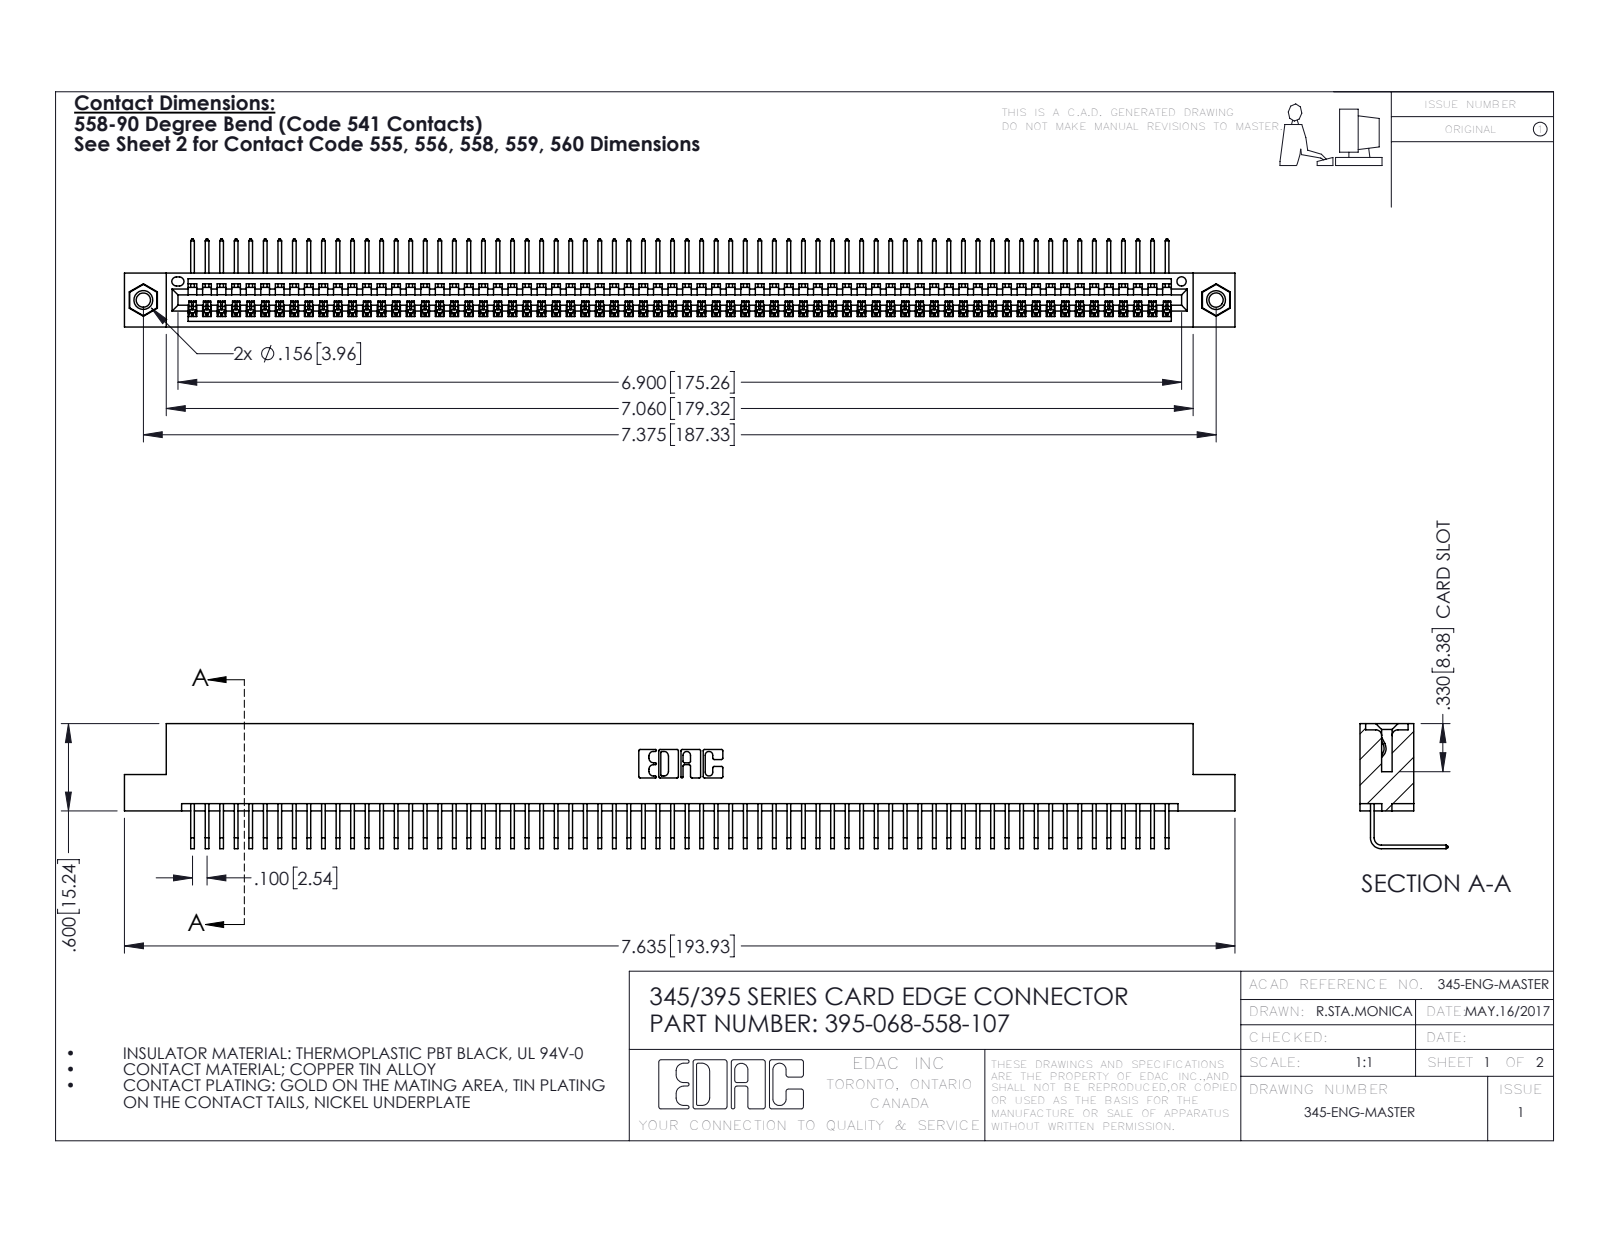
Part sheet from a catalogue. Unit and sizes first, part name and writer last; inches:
Units: inches
Overall size (bounding box): 7.635 × 0.859 × 0.605
Round holes (diameter × count): ⌀0.098 ×2, ⌀0.125 ×2, ⌀0.156 ×2, ⌀0.064 ×1
Round bosses / shafts (diameter × count): ⌀0.155 ×2
Partial cylindrical surfaces — rounded edges, fillets, slot ends (radius × count): R0.006 ×136, R0.01 ×22, R0.007 ×6, R0.031 ×6, R0.026 ×3, R0.031 ×2, R0.04 ×2, R0.014 ×1
Main face-to-face distances: 0.072, 0.298, 0.37, 0.2, 0.098, 0.272, 0.025, 0.225, 0.149, 0.072
Hole centre spacings: 0.27, 7.139, 7.375
Volume: 1.15 in³ · Surface area: 41.48 in²
Bodies: 71 solids, 4266 faces (2968 planar, 1282 cylindrical, 16 other)
Part name (STEP PRODUCT): 395-068-558-107; 345-250-001_345-250-005-103; 345-292-001_558 Tail - 2; 345 Part_Flush Mounting Lugs - 0.156 Dia-TI
STEP written by: SolidWorks 2016 (CONFIG_CONTROL_DESIGN)
